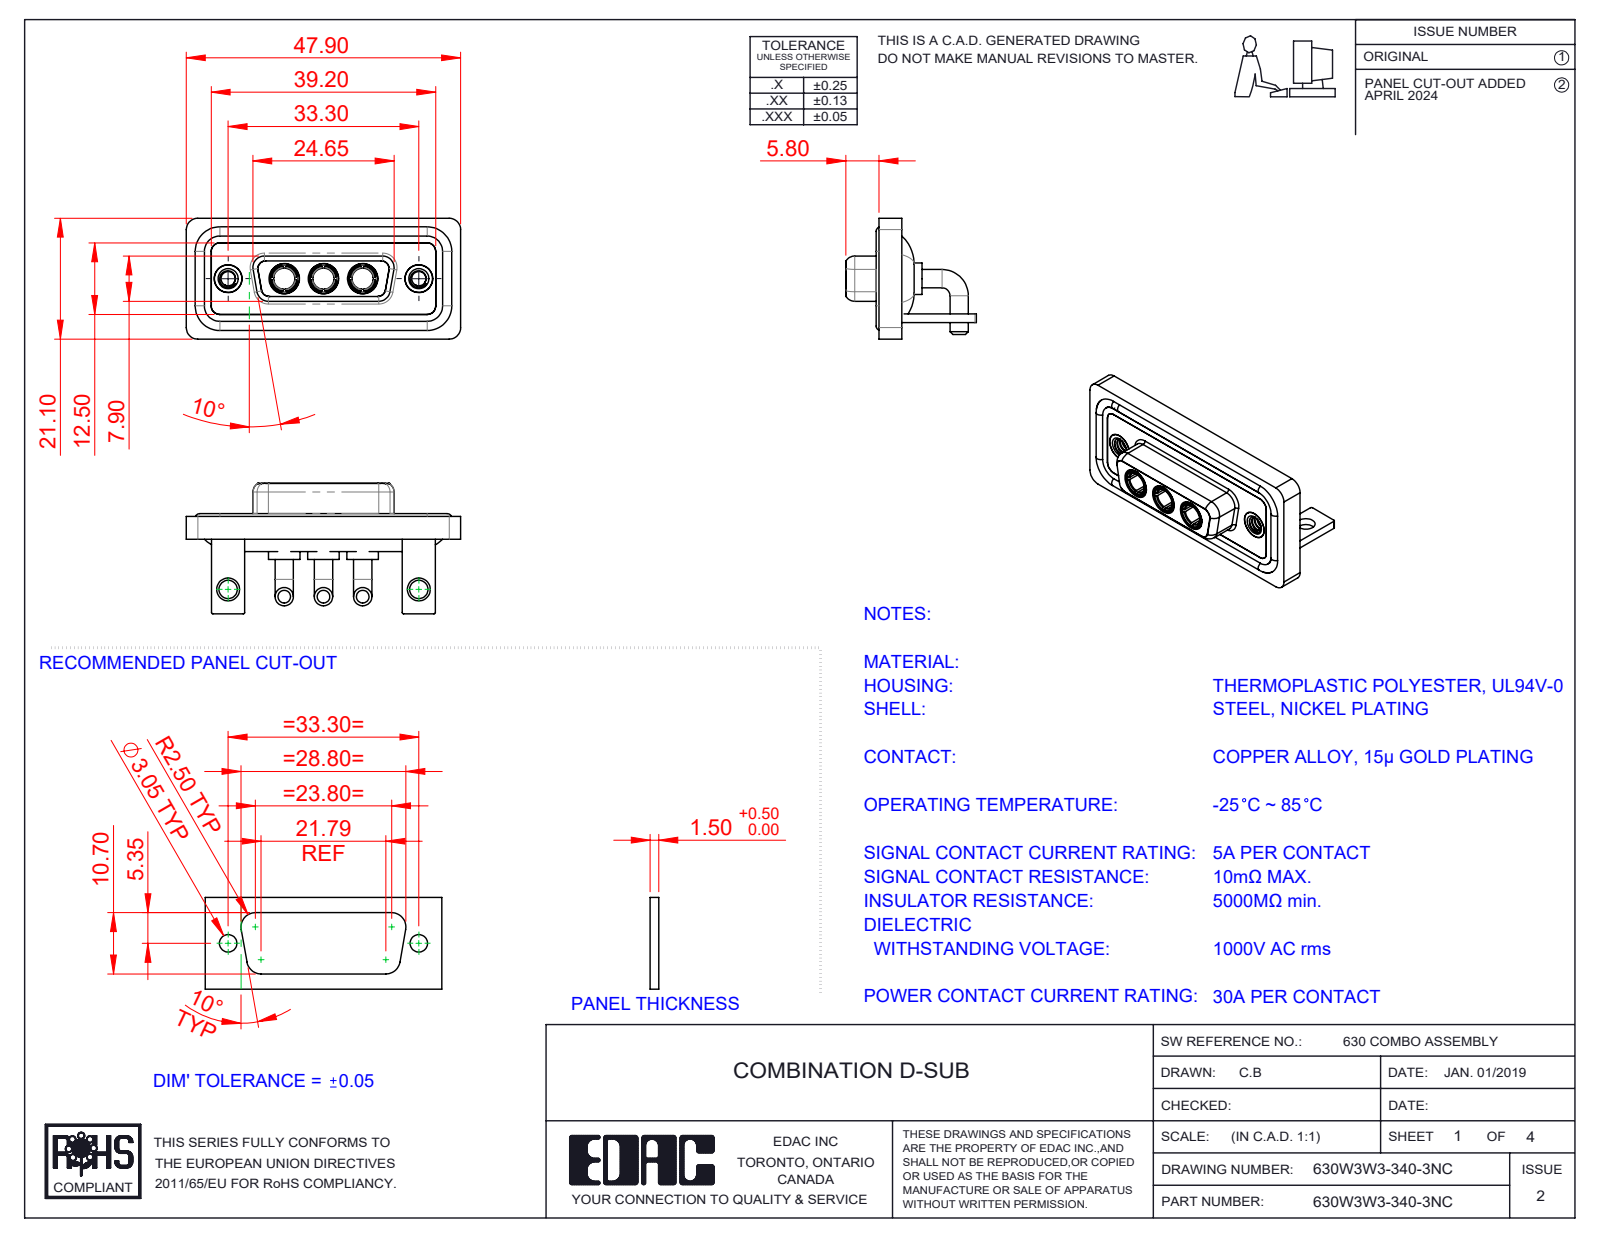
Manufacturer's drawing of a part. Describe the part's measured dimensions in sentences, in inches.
The part is named "630W3W3-340-3NC; 630Combo Stabilizer Bracket_50 Contacts; 630Combo Shell Front_15 Contacts; 630Combo Housing_3W3 (+4 more)". Its 3-D file was written by "SolidWorks 2023 (CONFIG_CONTROL_DESIGN)". It is 15 solids with 662 faces: 212 planar, 285 cylindrical and 165 other. Overall it measures 1.886 by 0.898 by 0.831 inches. Its volume is 0.404 cubic inches and its surface area 16.69 square inches. Round holes: 5 of diameter 0.191, 3 of diameter 0.146, 3 of diameter 0.209, 2 of diameter 0.098, 2 of diameter 0.126, 2 of diameter 0.157, 2 of diameter 0.159, 2 of diameter 0.197. Round bosses or shafts: 6 of diameter 0.126, 4 of diameter 0.063, 3 of diameter 0.217, 3 of diameter 0.205, 3 of diameter 0.195, 3 of diameter 0.187, 3 of diameter 0.148, 2 of diameter 0.195. Partial cylindrical surfaces (rounded edges, fillets, slot ends): 21 of radius 0.079, 18 of radius 0.059, 16 of radius 0.01, 12 of radius 0.053, 8 of radius 0.063, 5 of radius 0.02, 4 of radius 0.024, 4 of radius 0.026. The main face-to-face distances are 0.016, 0.114, 0.059, 0.071, 0.146, 0.043, 0.161, 0.063, 0.098, 0.055. The hole center spacings are 0.27, 0.386, 0.656, 0.925, 1.311, 0.539.
